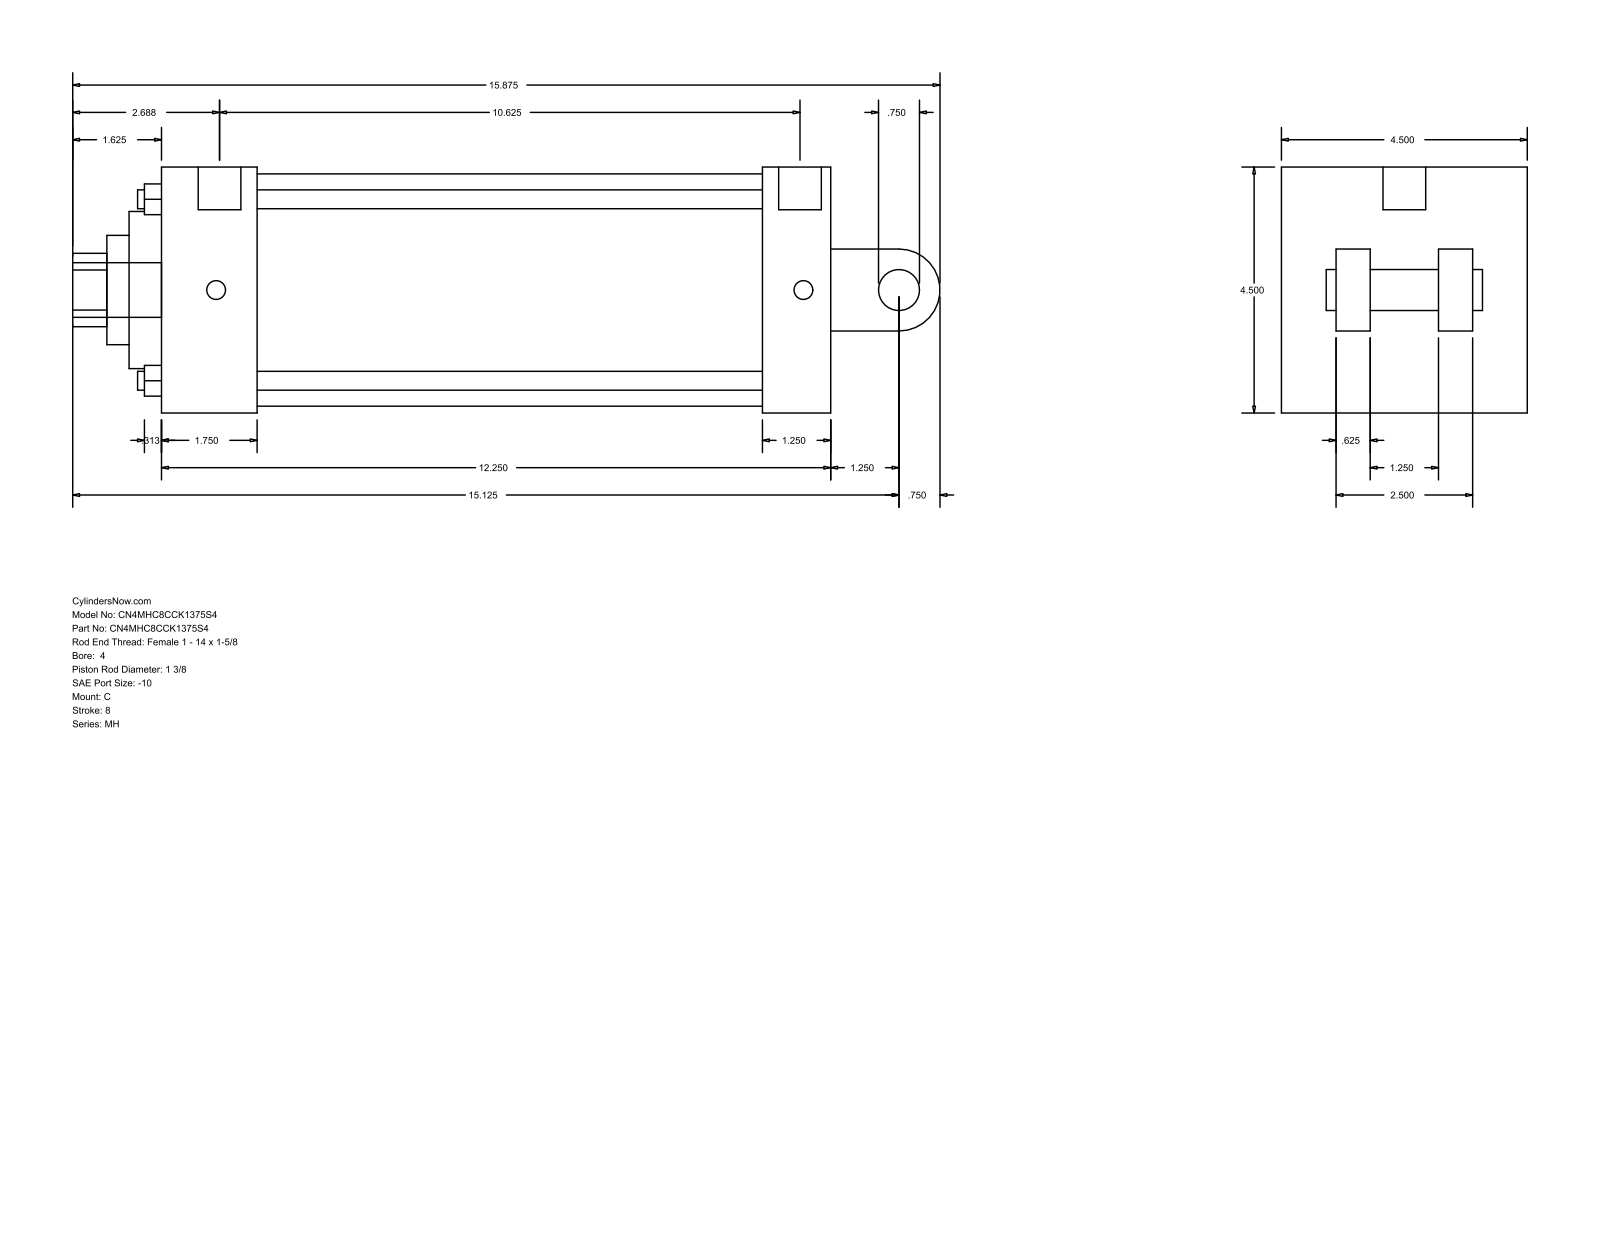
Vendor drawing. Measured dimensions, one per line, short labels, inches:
name: MH_C__0400_1.375
written by: GSSL Pune (CONFIG_CONTROL_DESIGN)
unit: in
bodies: 0 solids, 101 faces (71 planar, 30 cylindrical, 0 other)
size: 15.875 × 4.5 × 4.5
holes: 4× ⌀0.345, 2× ⌀0.344, 1× ⌀0.781, 1× ⌀1.375, 1× ⌀2, 1× ⌀2.875, 1× ⌀4.25
bosses: 2× ⌀0.344, 1× ⌀1, 1× ⌀0.781, 1× ⌀0.75
rounds: 1× R0.672, 1× R0.75
face distances: 4.5, 12.25, 1.75, 11, 9.25, 10.5, 1.25, 2.875, 1.625, 1.5
hole spacings: 2.347, 3.32, 4.695, 0.063
